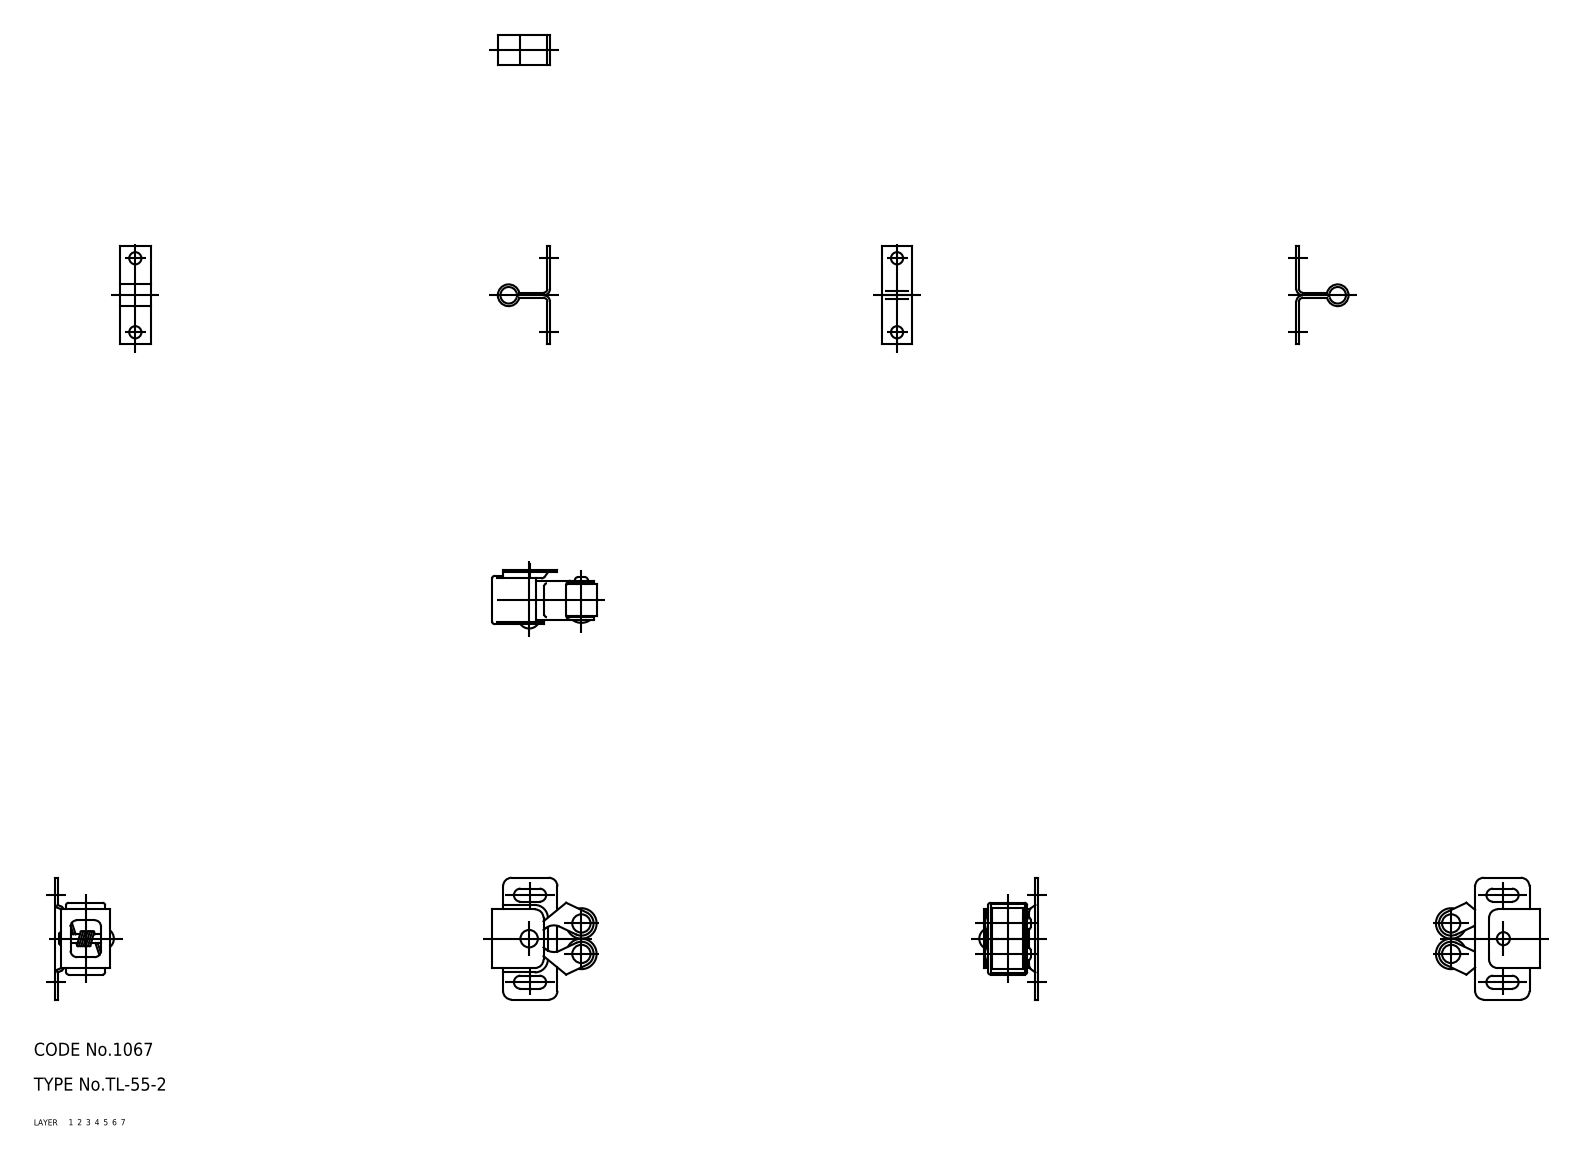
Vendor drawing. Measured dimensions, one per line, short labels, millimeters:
name: arm; roller; shaft_B; keeper (+4 more)
written by: CADfix (AUTOMOTIVE_DESIGN)
unit: mm
bodies: 10 solids, 267 faces (0 planar, 0 cylindrical, 267 other)
size: 40 × 28 × 13.5
volume: 1 562 mm³; area: 4 506 mm²
